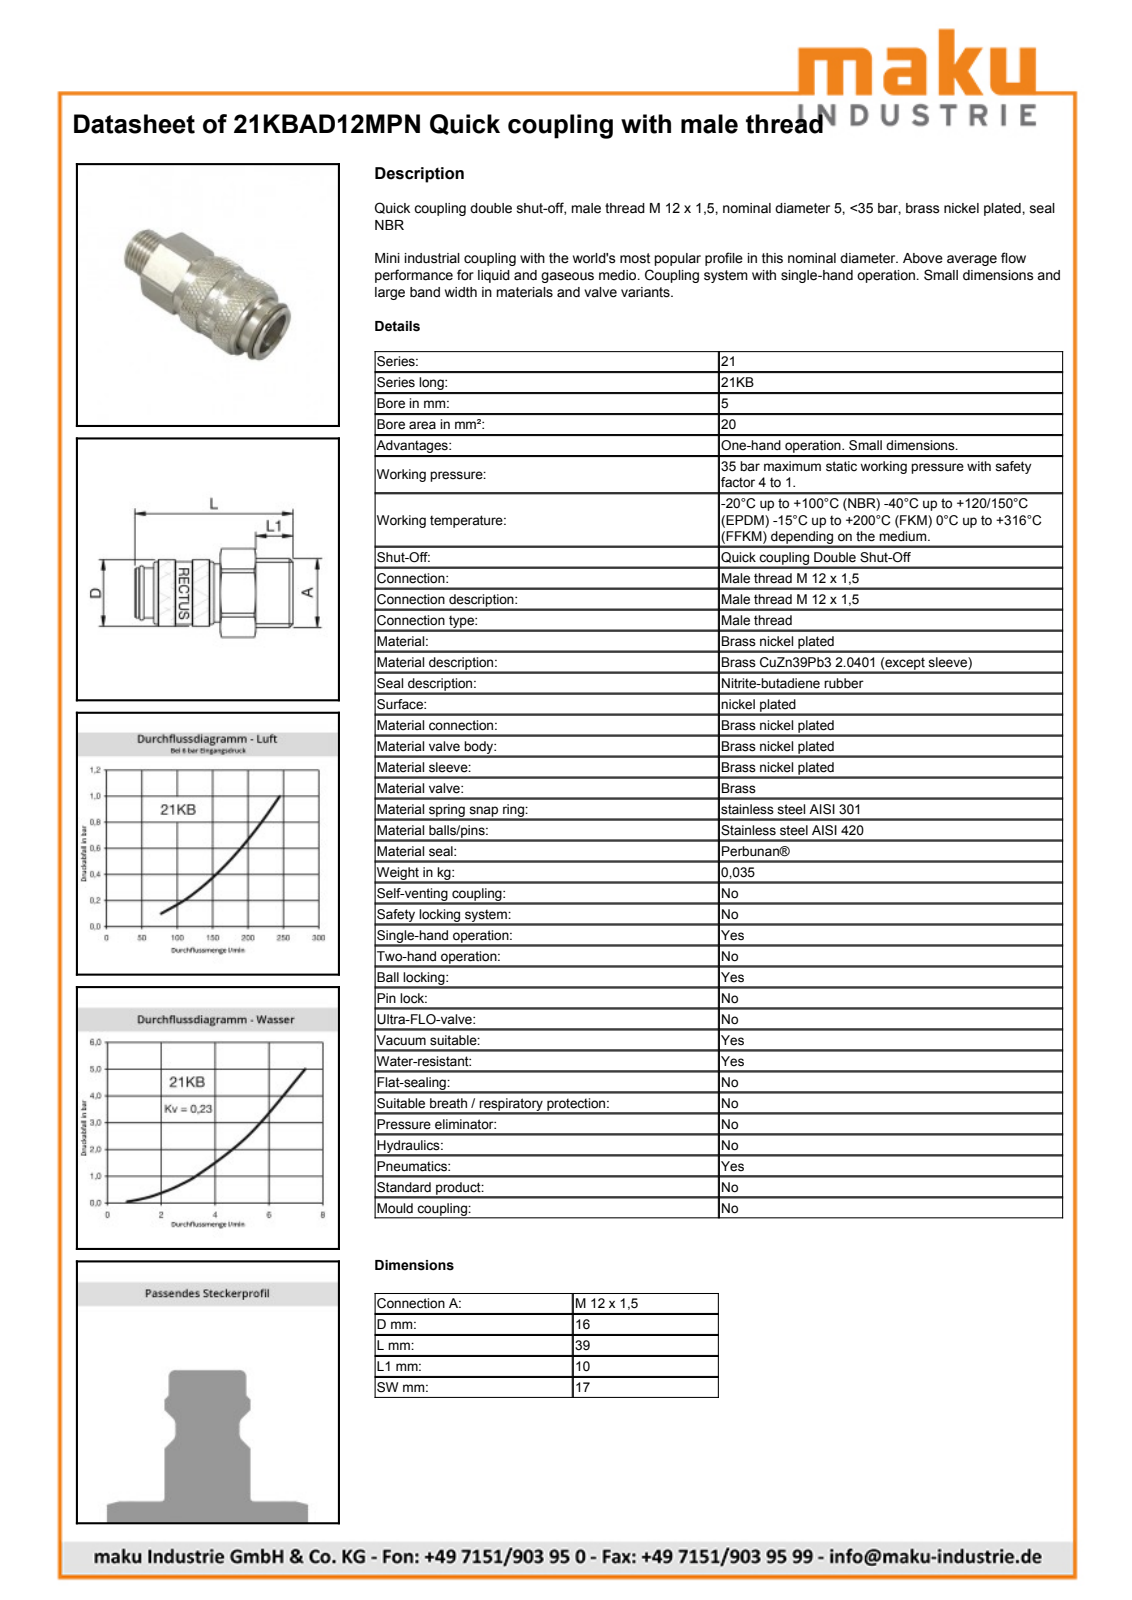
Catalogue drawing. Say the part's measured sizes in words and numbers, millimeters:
The part is named "D107237". Its 3-D file was written by "Autodesk Inventor 2013 (AUTOMOTIVE_DESIGN)". It is 2 solids with 446 faces: 150 planar, 56 cylindrical and 240 other. Overall it measures 39.06 by 19.15 by 17.05 millimeters. Its volume is 6 510 cubic millimeters and its surface area 3 322 square millimeters. Round holes: 1 of diameter 12.15, 1 of diameter 14. Round bosses or shafts: 1 of diameter 16.15, 1 of diameter 15.1, 1 of diameter 12.51, 1 of diameter 12, 1 of diameter 11.15, 1 of diameter 9.7. Partial cylindrical surfaces (rounded edges, fillets, slot ends): 1 of radius 7.45, 1 of radius 9.57. The main face-to-face distances are 17, 29.06, 10, 39.06, 20.51, 8.55, 18.55, 4.56, 15.95, 24.5.
